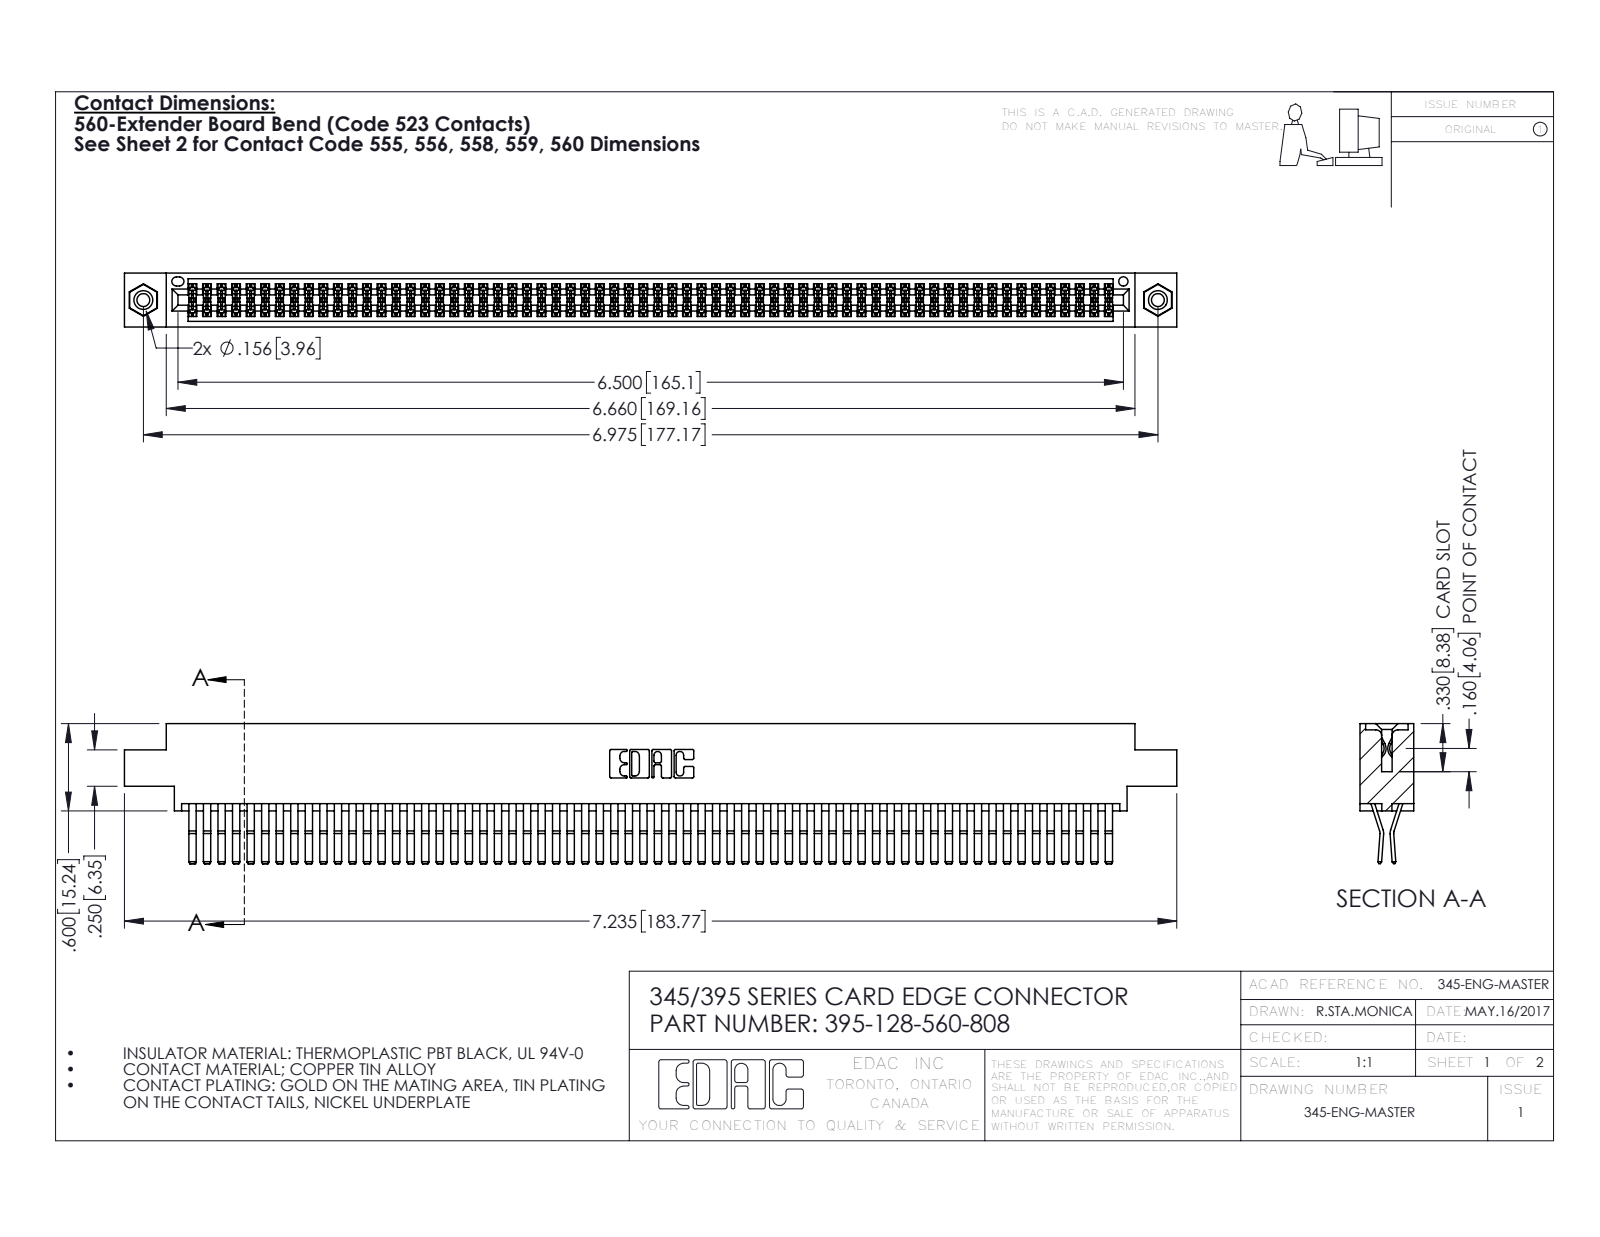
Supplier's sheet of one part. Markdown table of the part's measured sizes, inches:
| quantity | value |
| --- | --- |
| part name | 345 Part_0.170 Offset - 0.156 Dia-TI; 345-250-001_345-250-003-102; 345-292-001_560 Tail; 395-128-560-808 |
| STEP written by | SolidWorks 2016 (CONFIG_CONTROL_DESIGN) |
| units | inches |
| bodies | 131 solids, 6846 faces (4340 planar, 2490 cylindrical, 16 other) |
| overall size | 7.235 × 0.962 × 0.37 |
| volume | 1.146 in³ |
| surface area | 47.26 in² |
| round holes (diameter × count) | 0.089 × 2, 0.125 × 2, 0.156 × 2, 0.064 × 1 |
| round bosses / shafts (diameter × count) | 0.155 × 2 |
| partial cylindrical surfaces (radius × count) | 0.006 × 192, 0.01 × 22, 0.007 × 6, 0.031 × 6, 0.026 × 3, 0.01 × 2, 0.014 × 2, 0.019 × 2 |
| main face-to-face distances | 0.025, 0.072, 0.298, 0.37, 0.2, 0.098, 0.272, 0.225, 0.175, 0.149 |
| hole center spacings | 0.27, 6.739, 6.975 |
